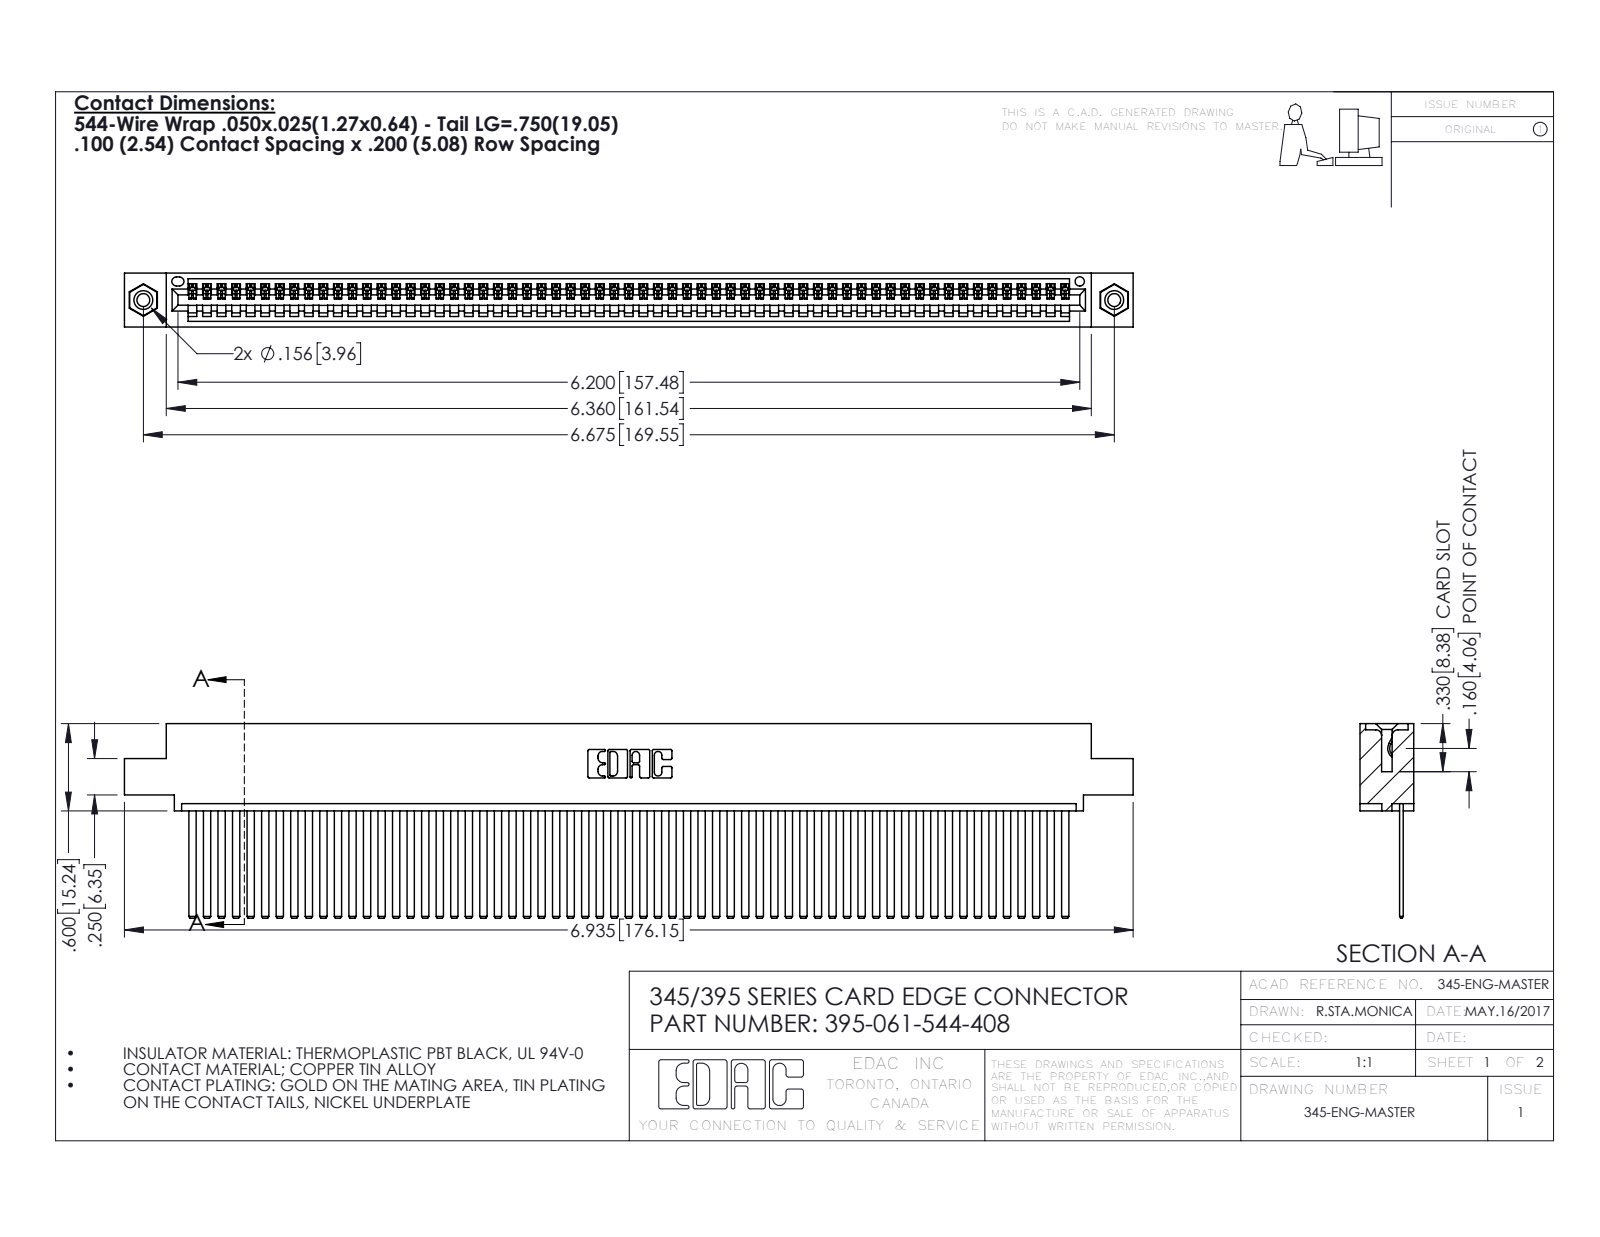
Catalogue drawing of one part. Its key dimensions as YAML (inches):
part_name: "345 Part_0.110 Offset - 0.156 Dia-TI; 395-061-544-408; 345-292-001_345-293-144; 345-250-001_345-250-003-102"
step_written_by: "SolidWorks 2016 (CONFIG_CONTROL_DESIGN)"
units: inches
bodies: {solids: 64, faces: 3362, planar: 2312, cylindrical: 1034, other: 16}
overall_size: [6.935, 1.337, 0.37]
volume: 1.069
surface_area: 39.92
round_holes:
  - {diameter: 0.089, count: 2}
  - {diameter: 0.125, count: 2}
  - {diameter: 0.156, count: 2}
  - {diameter: 0.064, count: 1}
round_bosses_or_shafts:
  - {diameter: 0.155, count: 2}
partial_cylinders:
  - {radius: 0.006, count: 122}
  - {radius: 0.01, count: 22}
  - {radius: 0.007, count: 6}
  - {radius: 0.031, count: 6}
  - {radius: 0.026, count: 3}
  - {radius: 0.031, count: 2}
  - {radius: 0.04, count: 2}
  - {radius: 0.014, count: 1}
face_to_face_distances: [0.072, 0.298, 0.025, 0.098, 0.272, 0.37, 0.2, 0.225, 0.149, 0.072]
hole_center_spacings: [0.27, 6.439, 6.675]
